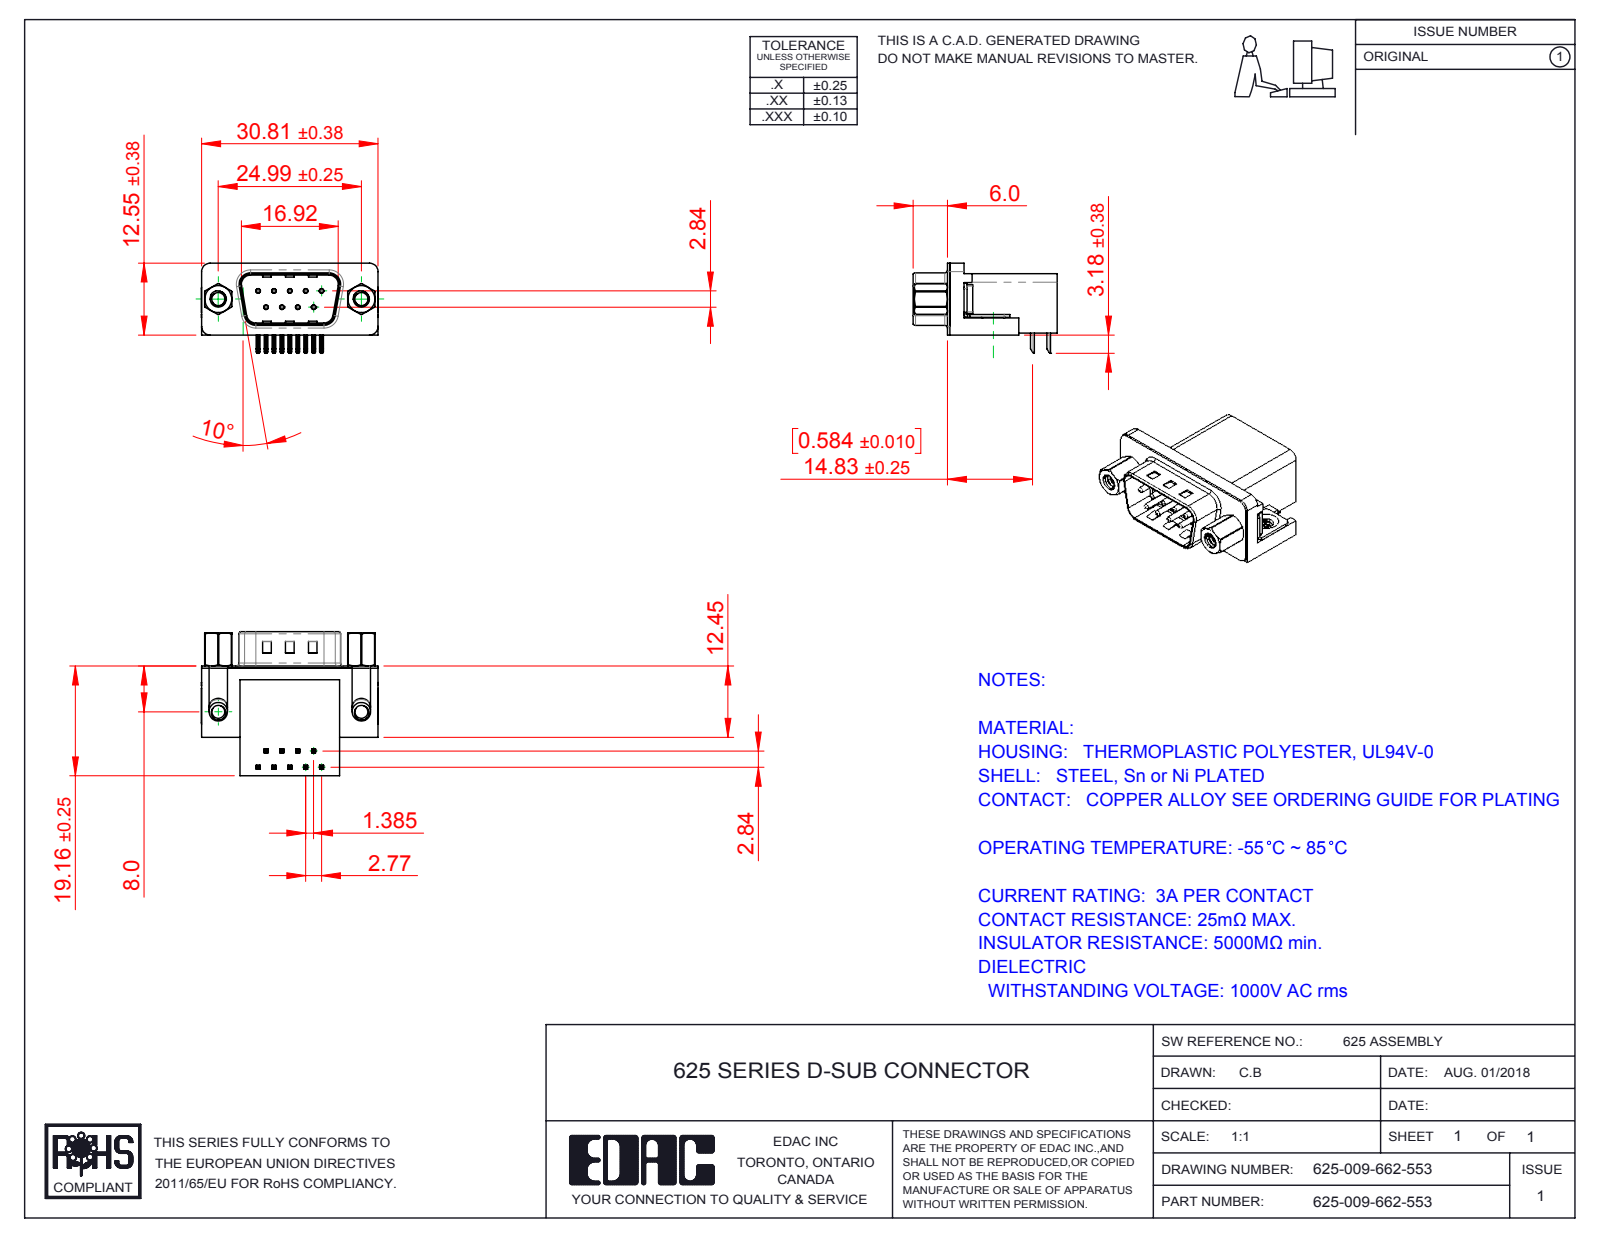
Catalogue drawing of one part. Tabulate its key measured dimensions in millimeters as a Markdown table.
| quantity | value |
| --- | --- |
| part name | 625 Shell_9 Socket; 625 4-40 Threaded Rivet; 625 4-40 Threaded Board Mount; 625 4-40 Hex Standoff 5 (+4 more) |
| STEP written by | SolidWorks 2016 (CONFIG_CONTROL_DESIGN) |
| units | millimeters |
| bodies | 17 solids, 1151 faces (597 planar, 401 cylindrical, 153 other) |
| overall size | 30.89 × 25.16 × 15.73 |
| volume | 4 700 mm³ |
| surface area | 5 514 mm² |
| round holes (diameter × count) | 0.35 × 9, 0.8 × 9, 2.26 × 4, 2.29 × 2, 4 × 2, 4.8 × 2, 5 × 2 |
| round bosses / shafts (diameter × count) | 0.75 × 9, 4.9 × 2, 4.75 × 2, 3.9 × 2, 3.26 × 2, 2.79 × 2 |
| partial cylindrical surfaces (radius × count) | 0.25 × 44, 0.12 × 18, 1 × 16, 0.5 × 9, 1.5 × 8, 1.6 × 8, 0.9 × 4, 2 × 4 |
| main face-to-face distances | 0.4, 10.34, 18.76, 19.16, 16.26, 2.5, 2.9, 0.35, 10.69, 6.7 |
| hole center spacings | 3.16, 2.77, 5.54, 5.03, 5.04, 8.31, 7.48, 7.49 |
